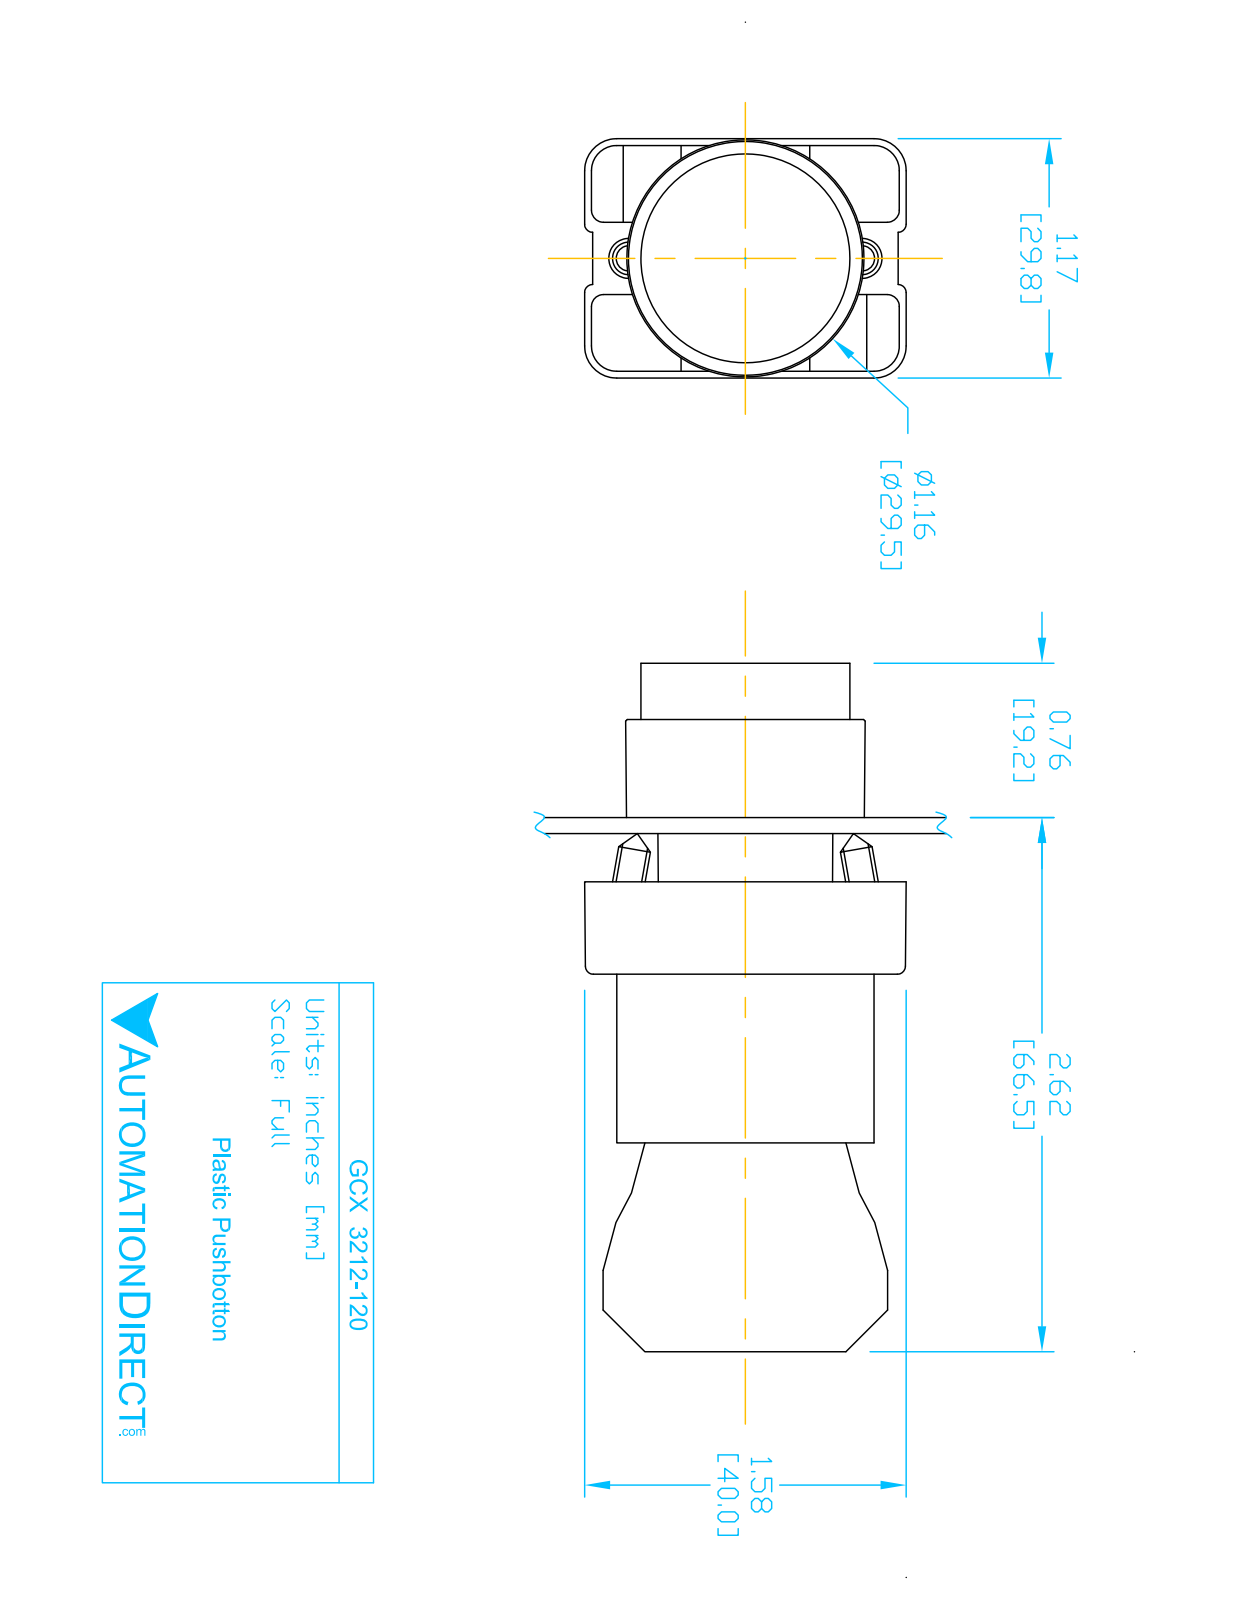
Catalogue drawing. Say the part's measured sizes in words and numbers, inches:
The part is named "ecx1040; GCX3212 OPERATOR; ECX3029-2; ECX1050 (+1 more)". Its 3-D file was written by "SolidWorks 2016 (AUTOMOTIVE_DESIGN)". It is 7 solids with 425 faces: 250 planar, 144 cylindrical and 31 other. Overall it measures 3.319 by 1.581 by 1.177 inches. Its volume is 2.721 cubic inches and its surface area 36.32 square inches. Round holes: 2 of diameter 0.079, 2 of diameter 0.124, 2 of diameter 0.13, 1 of diameter 0.087, 1 of diameter 0.197, 1 of diameter 0.469, 1 of diameter 0.878, 1 of diameter 0.888, 1 of diameter 1.024. Round bosses or shafts: 4 of diameter 0.157, 1 of diameter 1.175, 1 of diameter 1.004, 1 of diameter 0.945, 1 of diameter 0.856, 1 of diameter 0.78, 1 of diameter 0.504. Partial cylindrical surfaces (rounded edges, fillets, slot ends): 24 of radius 0.059, 12 of radius 0.041, 12 of radius 0.124, 12 of radius 0.157, 8 of radius 0.039, 2 of radius 0.128, 1 of radius 0.02, 1 of radius 0.063. The main face-to-face distances are 0.827, 0.579, 1.171, 2.02, 1.193, 0.031, 0.033, 0.573, 1.165, 0.593. The hole center spacings are 0.236, 0.544, 0.472, 0.49.
